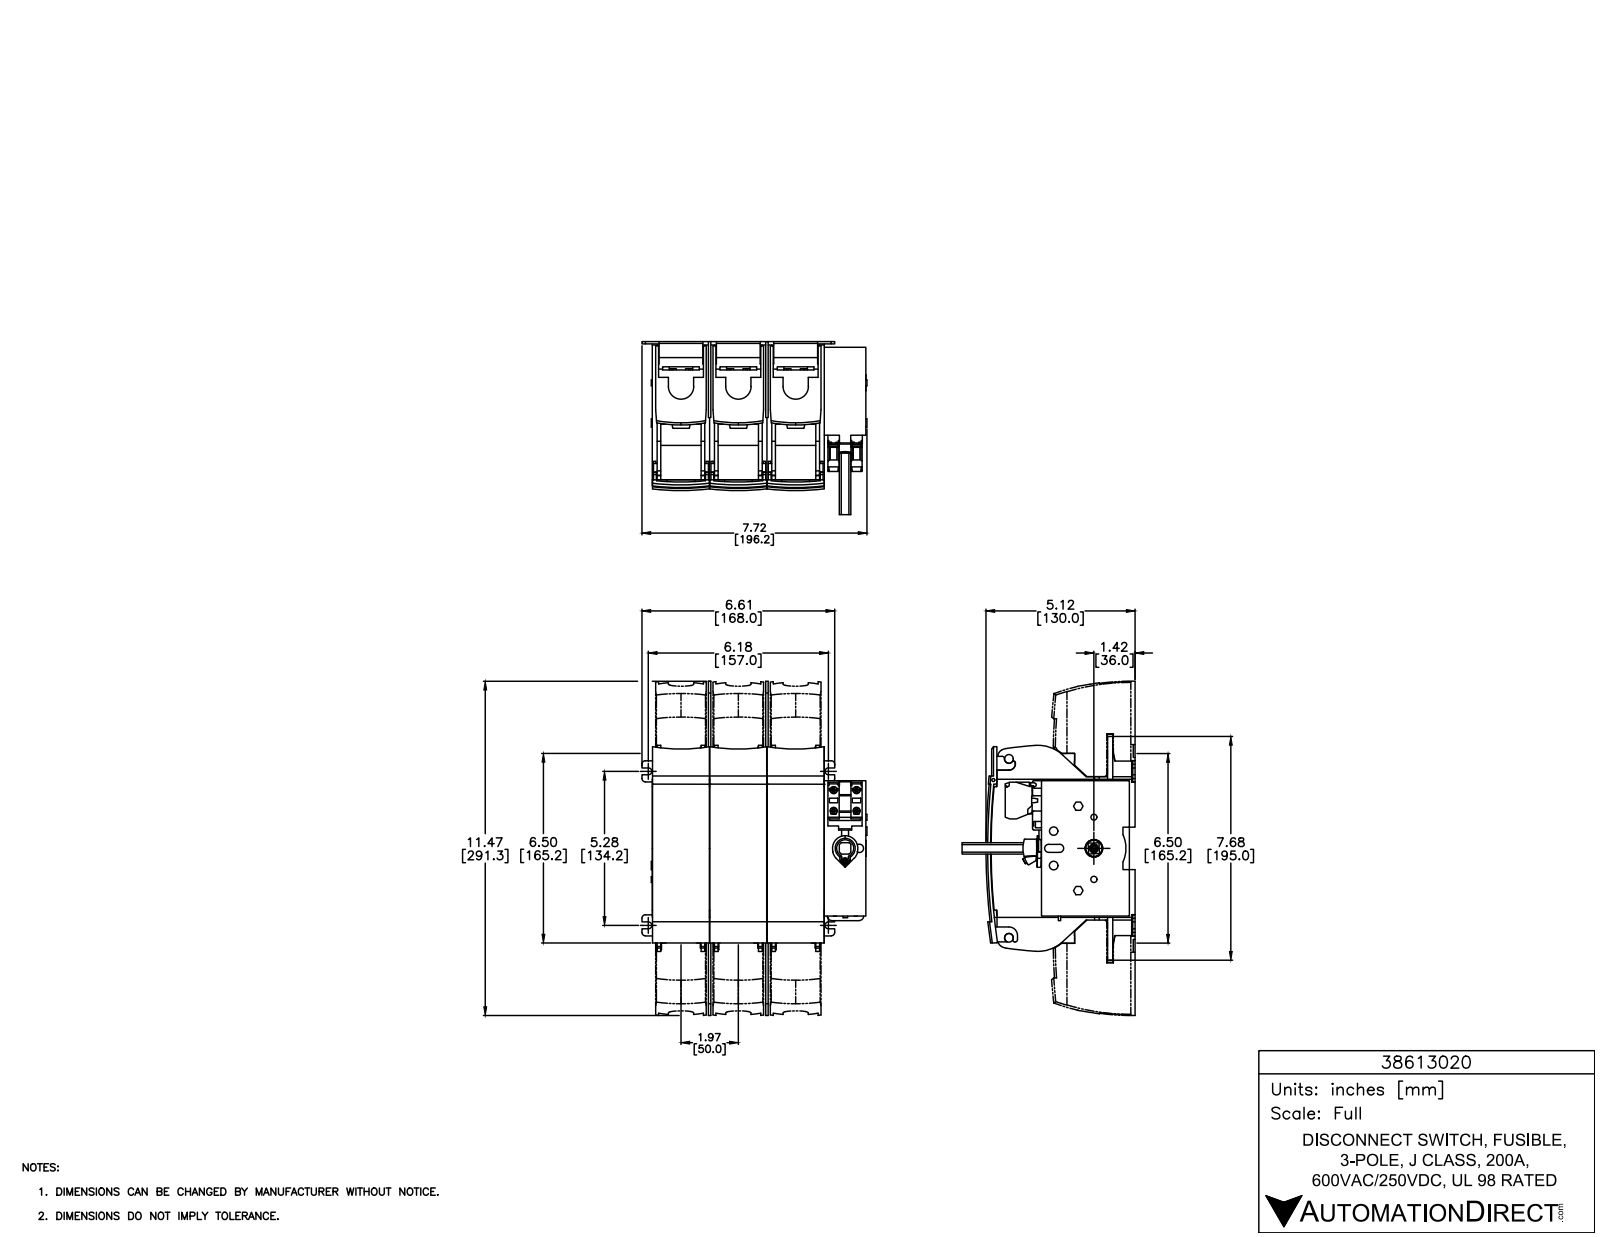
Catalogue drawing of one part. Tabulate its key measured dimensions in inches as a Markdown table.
| quantity | value |
| --- | --- |
| part name | 38613020 |
| STEP written by | SolidWorks 2015 (AUTOMOTIVE_DESIGN) |
| units | inches |
| bodies | 16 solids, 1706 faces (1163 planar, 416 cylindrical, 127 other) |
| overall size | 11.469 × 7.724 × 5.118 |
| volume | 185.3 in³ |
| surface area | 649.3 in² |
| round holes (diameter × count) | 0.276 × 6, 0.433 × 6, 0.209 × 2, 0.211 × 2, 0.295 × 2, 0.315 × 2, 0.098 × 1, 0.102 × 1, 0.13 × 1, 0.283 × 1, 0.602 × 1, 0.622 × 1 |
| round bosses / shafts (diameter × count) | 0.295 × 2, 0.287 × 2, 0.205 × 2, 0.203 × 2, 0.63 × 1, 0.315 × 1, 0.197 × 1 |
| partial cylindrical surfaces (radius × count) | 0.059 × 24, 0.118 × 12, 0.069 × 6, 0.079 × 6, 0.213 × 6, 0.295 × 6, 0.039 × 5, 0.138 × 4 |
| main face-to-face distances | 1.969, 0.041, 2.01, 1.927, 3.937, 0.083, 3.978, 3.896, 0.165, 1.803 |
| hole center spacings | 1.969, 6.795, 6.504, 0.653, 1.067, 1.204, 1.458, 1.499 |
